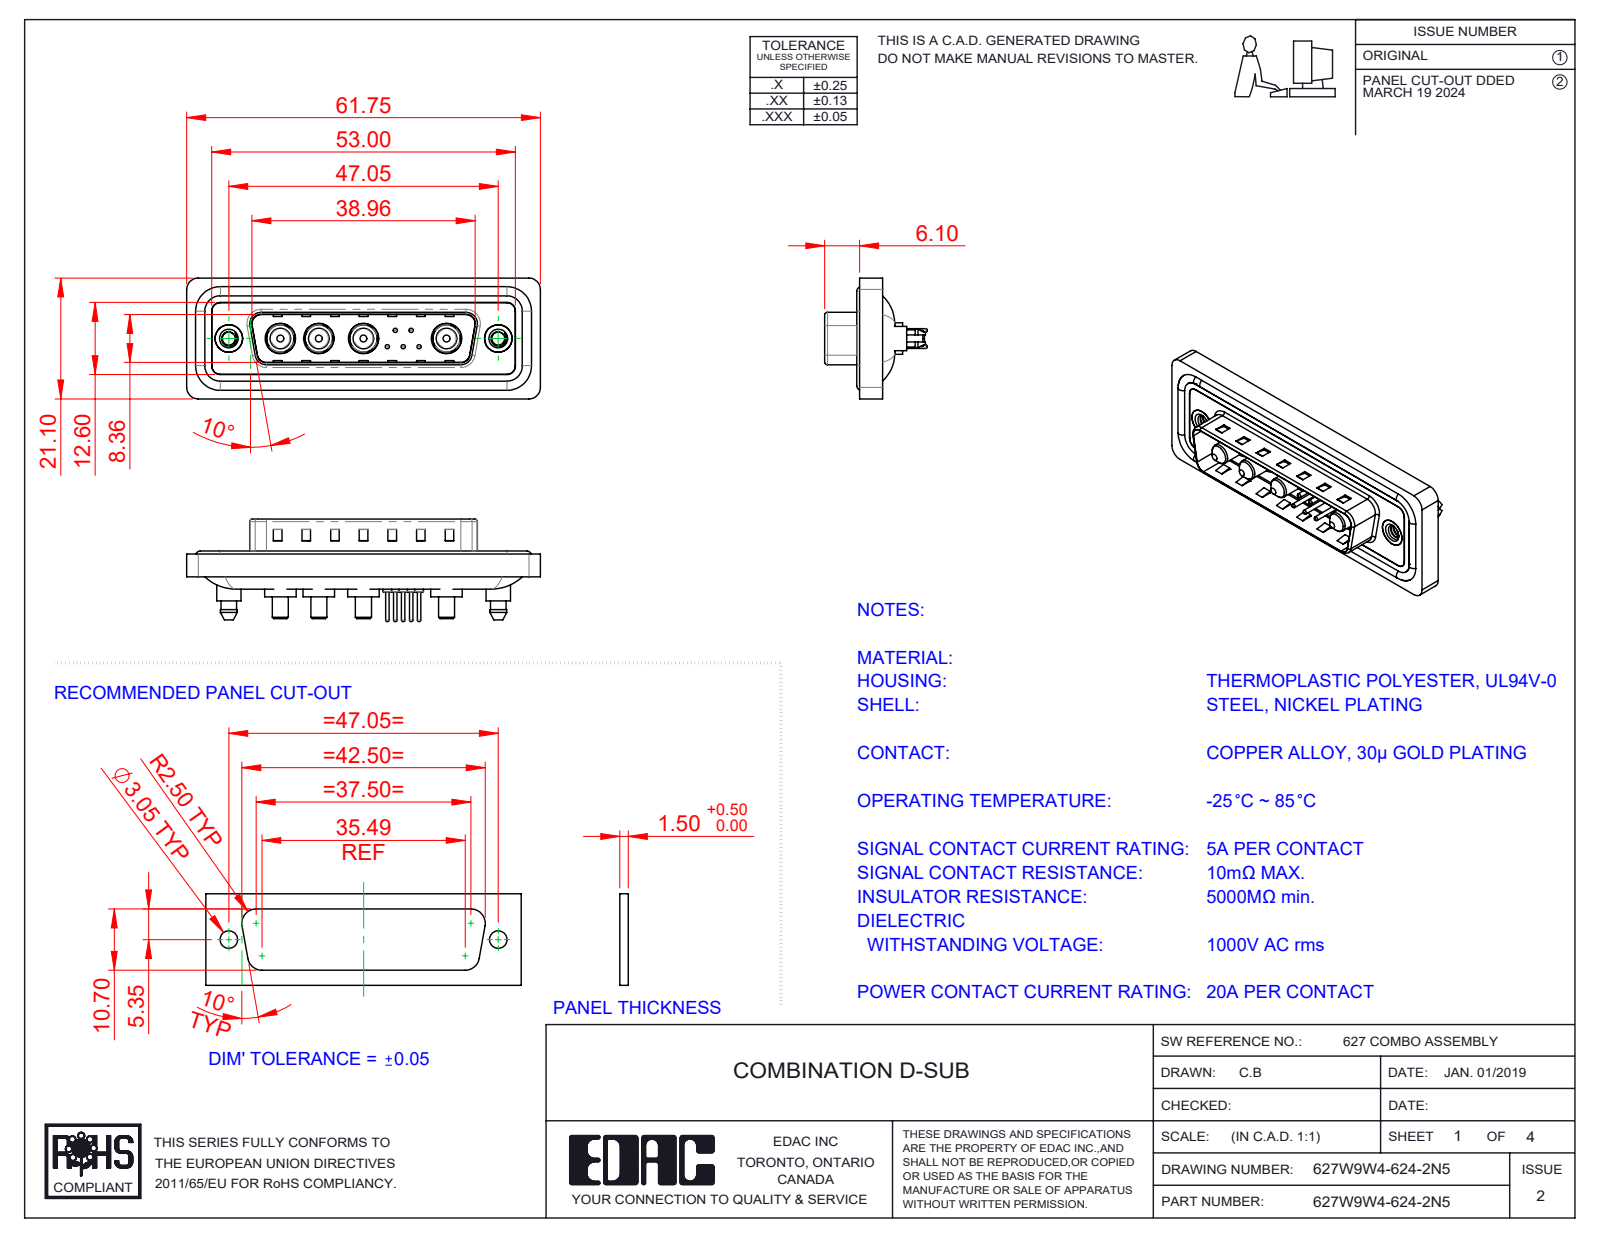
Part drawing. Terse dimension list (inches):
name: 627Combo Housing_9W4; 627Combo Waterproof Housing_25 Contacts; 627Combo Threaded Boardlock_5; 627Combo Contact Row 2_24 (+5 more)
written by: SolidWorks 2023 (CONFIG_CONTROL_DESIGN)
unit: in
bodies: 20 solids, 874 faces (300 planar, 366 cylindrical, 208 other)
size: 2.431 × 0.831 × 0.705
volume: 0.46 in³; area: 18.86 in²
holes: 5× ⌀0.03, 5× ⌀0.063, 5× ⌀0.079, 4× ⌀0.191, 4× ⌀0.209, 2× ⌀0.089, 2× ⌀0.157, 2× ⌀0.189, 2× ⌀0.197
bosses: 5× ⌀0.059, 5× ⌀0.024, 4× ⌀0.217, 4× ⌀0.205, 4× ⌀0.187, 4× ⌀0.148, 4× ⌀0.142, 4× ⌀0.11
rounds: 24× R0.059, 18× R0.079, 10× R0.063, 8× R0.02, 4× R0.01, 4× R0.024, 4× R0.026, 4× R0.035
face distances: 0.016, 0.059, 0.043, 0.02, 0.122, 0.063, 0.114, 0.032, 0.377, 0.222
hole spacings: 0.124, 0.109, 0.198, 0.571, 0.109, 0.173, 0.174, 0.197
